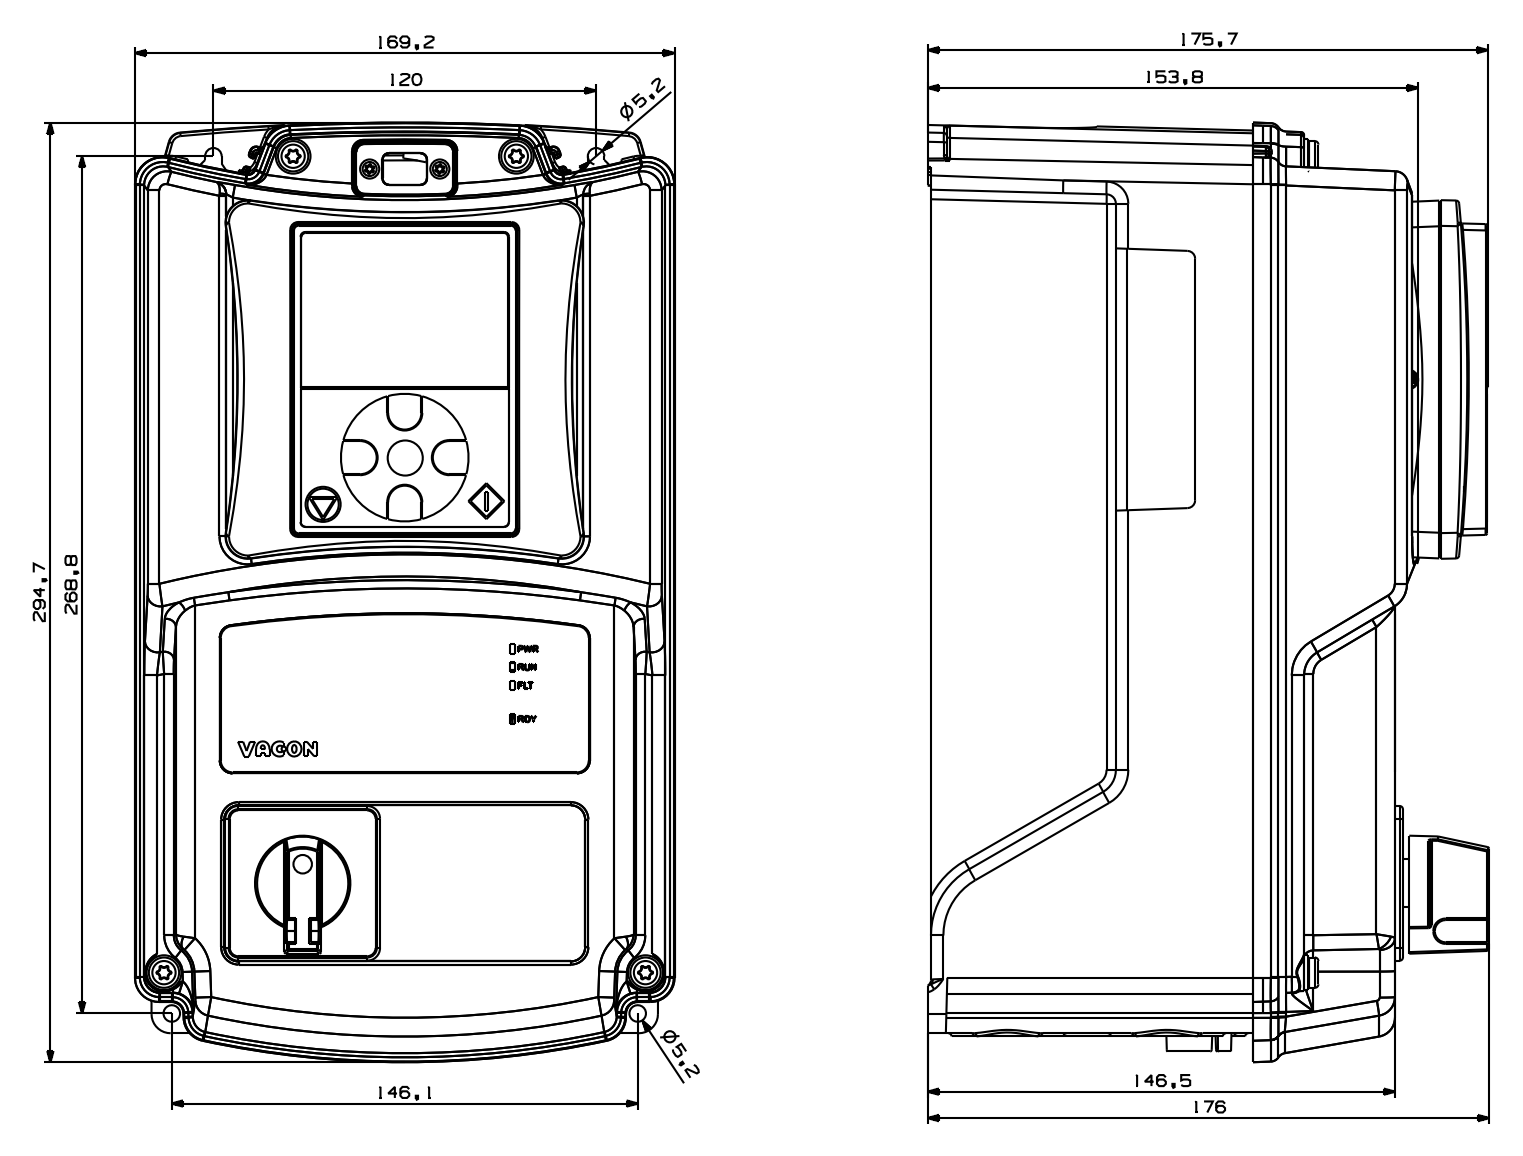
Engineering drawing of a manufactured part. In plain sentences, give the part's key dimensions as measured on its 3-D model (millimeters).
The part is named "CAD-3D-VACON20XD-MU2; CAD-3D-VACON20XD-MU2.sldasm-Part-1_Standard; CAD-3D-VACON20XD-MU2.sldasm-Part-2_Standard; CAD-3D-VACON20XD-MU2.sldasm-Part-3_Standard (+8 more)". Its 3-D file was written by "SolidWorks 2007 (CONFIG_CONTROL_DESIGN)". It is 45 solids with 9896 faces: 2686 planar, 2463 cylindrical and 4747 other. Overall it measures 294.69 by 176 by 169.21 millimeters. Its volume is 1 554 000 cubic millimeters and its surface area 963 116 square millimeters. Round holes: 6 of diameter 6, 5 of diameter 4, 4 of diameter 3.3, 4 of diameter 4.13, 4 of diameter 8, 3 of diameter 14.5, 3 of diameter 16, 2 of diameter 2.46, 2 of diameter 2.6, 2 of diameter 3, 2 of diameter 3.24, 2 of diameter 4.2. Round bosses or shafts: 13 of diameter 5, 8 of diameter 8, 4 of diameter 10.9, 4 of diameter 9.5, 4 of diameter 4.3, 4 of diameter 4.2, 4 of diameter 4, 2 of diameter 6.9. Partial cylindrical surfaces (rounded edges, fillets, slot ends): 282 of radius 0.5, 278 of radius 1, 169 of radius 0.2, 71 of radius 2, 50 of radius 1.5, 45 of radius 3, 43 of radius 0.3, 36 of radius 0.33. The main face-to-face distances are 10, 20, 30, 40, 50, 4, 60, 70, 80, 90. The hole center spacings are 2.65, 15.55, 18.03, 33.56, 36, 37.08, 41.06, 41.15.
